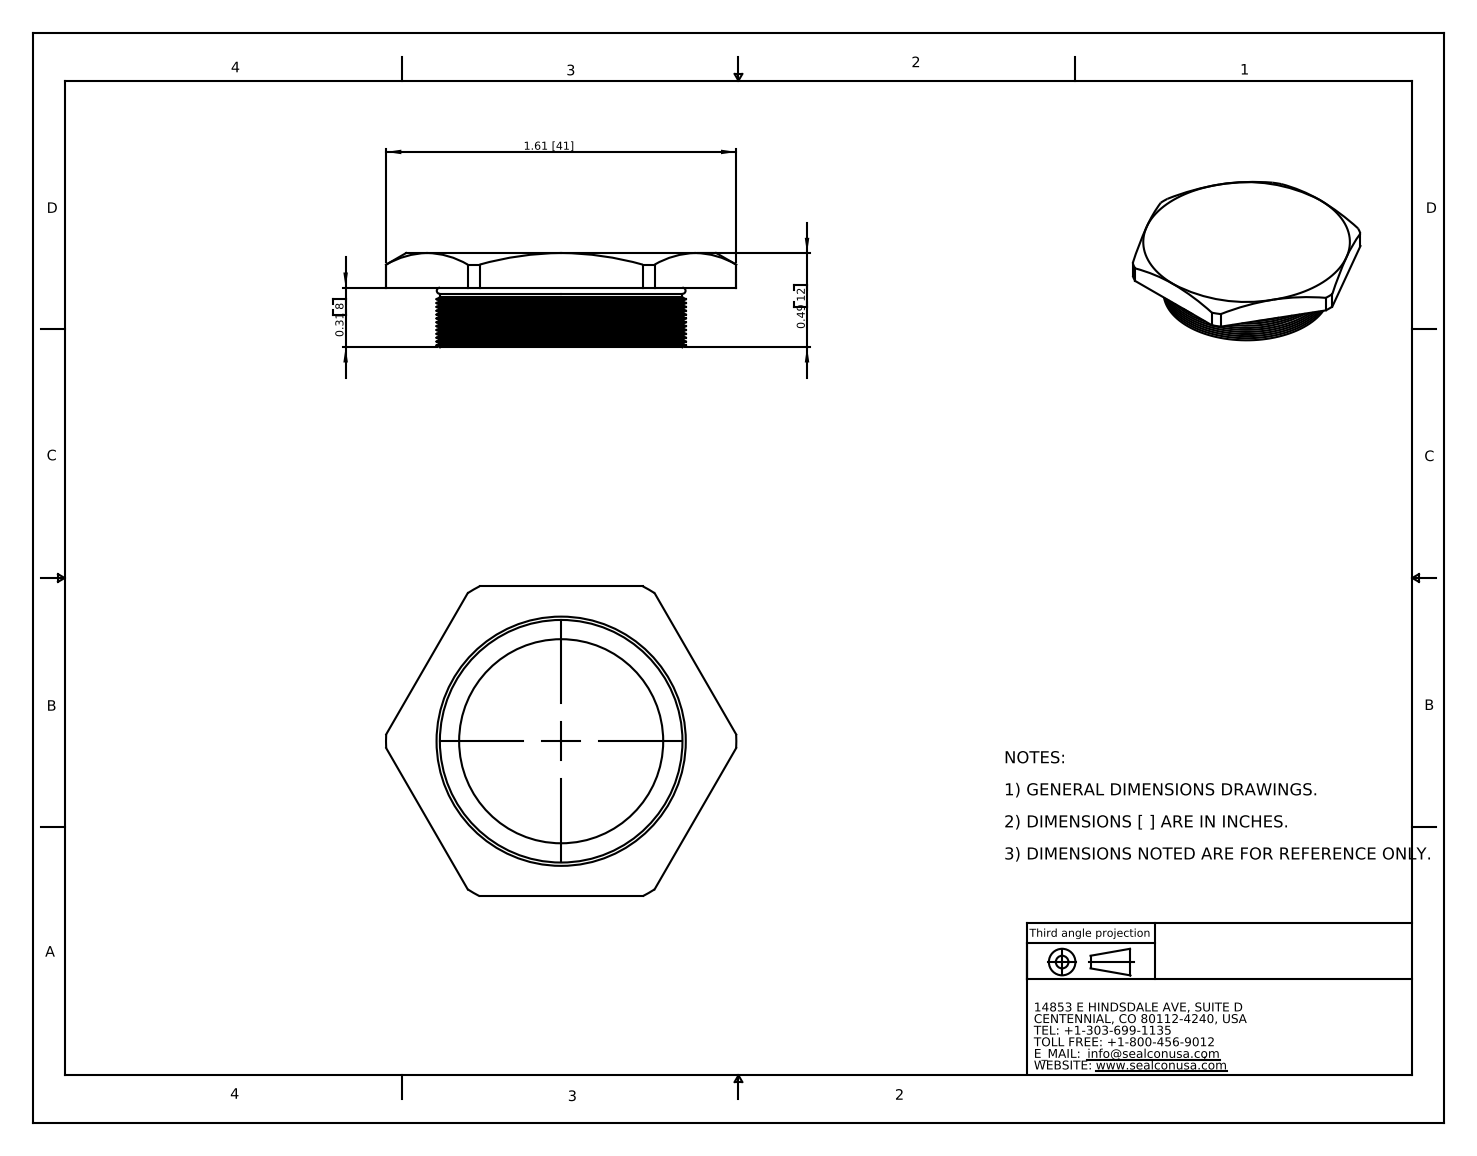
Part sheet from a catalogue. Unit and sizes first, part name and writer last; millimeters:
Units: millimetres
Overall size (bounding box): 46.2 × 40.9 × 12.4
Round holes (diameter × count): ⌀26.9 ×1
Round bosses / shafts (diameter × count): ⌀32 ×1
Partial cylindrical surfaces — rounded edges, fillets, slot ends (radius × count): R23.1 ×1
Main face-to-face distances: 4.6, 40.9, 7.9, 12.4
Volume: 8 570 mm³ · Surface area: 5 656 mm²
Bodies: 1 solid, 80 faces (10 planar, 10 cylindrical, 60 other)
Part name (STEP PRODUCT): HM-32-SS-S
STEP written by: SolidWorks 2007 (CONFIG_CONTROL_DESIGN)
